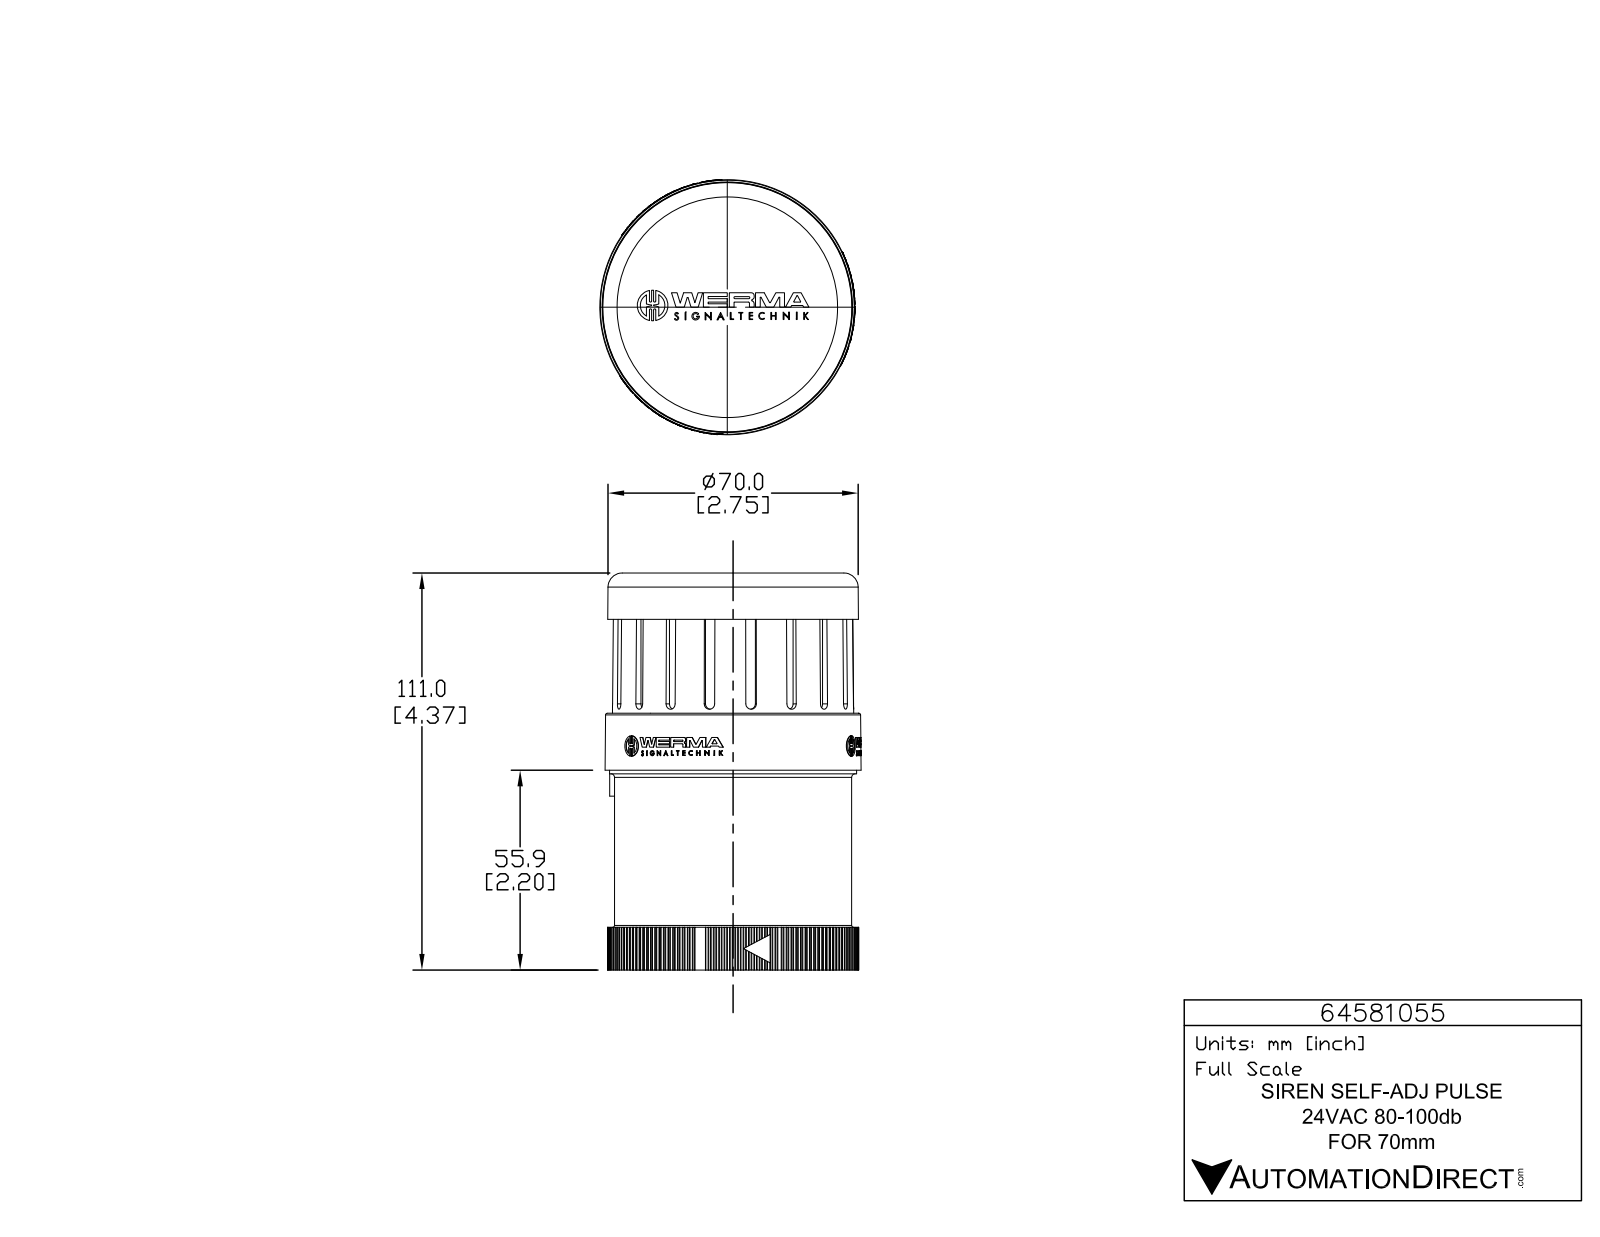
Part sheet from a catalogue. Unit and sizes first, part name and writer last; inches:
Units: inches
Overall size (bounding box): 4.382 × 2.817 × 2.815
Round holes (diameter × count): ⌀0.039 ×3, ⌀0.084 ×1, ⌀0.339 ×1, ⌀2.575 ×1
Round bosses / shafts (diameter × count): ⌀0.226 ×3, ⌀0.056 ×3, ⌀2.717 ×1, ⌀2.606 ×1, ⌀0.059 ×1
Partial cylindrical surfaces — rounded edges, fillets, slot ends (radius × count): R0.008 ×285, R0.059 ×16, R0.008 ×6, R0.008 ×6, R0.008 ×6, R0.131 ×6, R0.004 ×3, R0.005 ×3
Main face-to-face distances: 4.004, 0.118, 2.451, 0.378, 4.382, 2.452, 3.87, 3.492, 0.512, 2.205
Hole centre spacings: 0.363, 0.49, 0.825
Volume: 22.54 in³ · Surface area: 56.99 in²
Bodies: 1 solid, 1771 faces (1067 planar, 596 cylindrical, 108 other)
Part name (STEP PRODUCT): 64581055
STEP written by: SolidWorks 2015 (AUTOMOTIVE_DESIGN)
